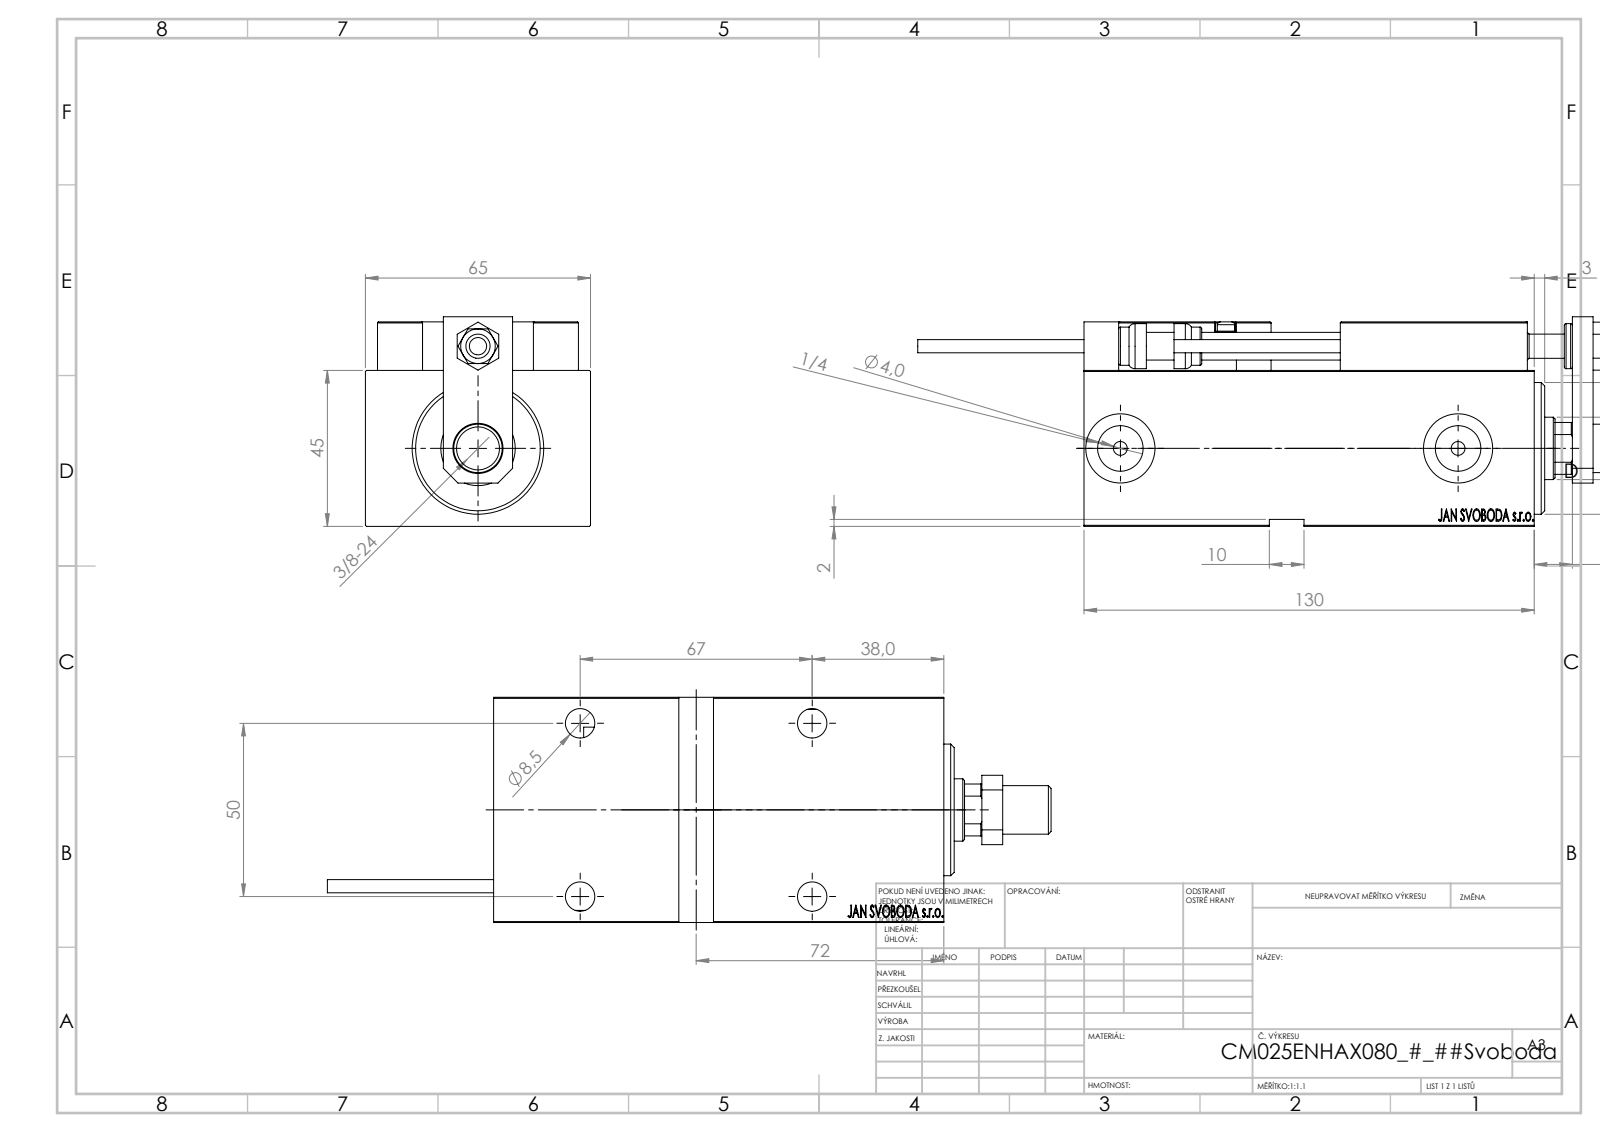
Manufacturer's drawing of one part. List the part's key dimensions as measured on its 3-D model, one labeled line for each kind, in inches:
Part name (STEP PRODUCT): KONCOVKA; TYC_L79; SWITCH X; NUT_D10 (+8 more)
STEP written by: SolidWorks 2019 (CONFIG_CONTROL_DESIGN)
Units: inches
Bodies: 25 solids, 1306 faces (573 planar, 186 cylindrical, 547 other)
Overall size (bounding box): 8.228 × 2.559 × 2.382
Volume: 24.36 in³ · Surface area: 141.5 in²
Round holes (diameter × count): ⌀0.157 ×6, ⌀0.315 ×5, ⌀0.335 ×5, ⌀0.126 ×4, ⌀0.531 ×4, ⌀0.197 ×2, ⌀0.518 ×2, ⌀0.787 ×2, ⌀0.276 ×1, ⌀0.571 ×1, ⌀0.709 ×1, ⌀0.846 ×1
Round bosses / shafts (diameter × count): ⌀0.197 ×2, ⌀0.15 ×2, ⌀1.496 ×1, ⌀1.063 ×1, ⌀0.551 ×1, ⌀0.512 ×1, ⌀0.472 ×1, ⌀0.433 ×1
Partial cylindrical surfaces — rounded edges, fillets, slot ends (radius × count): R0.012 ×30, R0.118 ×2, R0.335 ×1
Main face-to-face distances: 1.772, 2.559, 0.551, 0.236, 2.323, 5.118, 5.551, 0.512, 0.138, 0.748
Hole centre spacings: 1.587, 0.448, 0.787, 0.984, 1.165, 1.169, 1.356, 1.42
